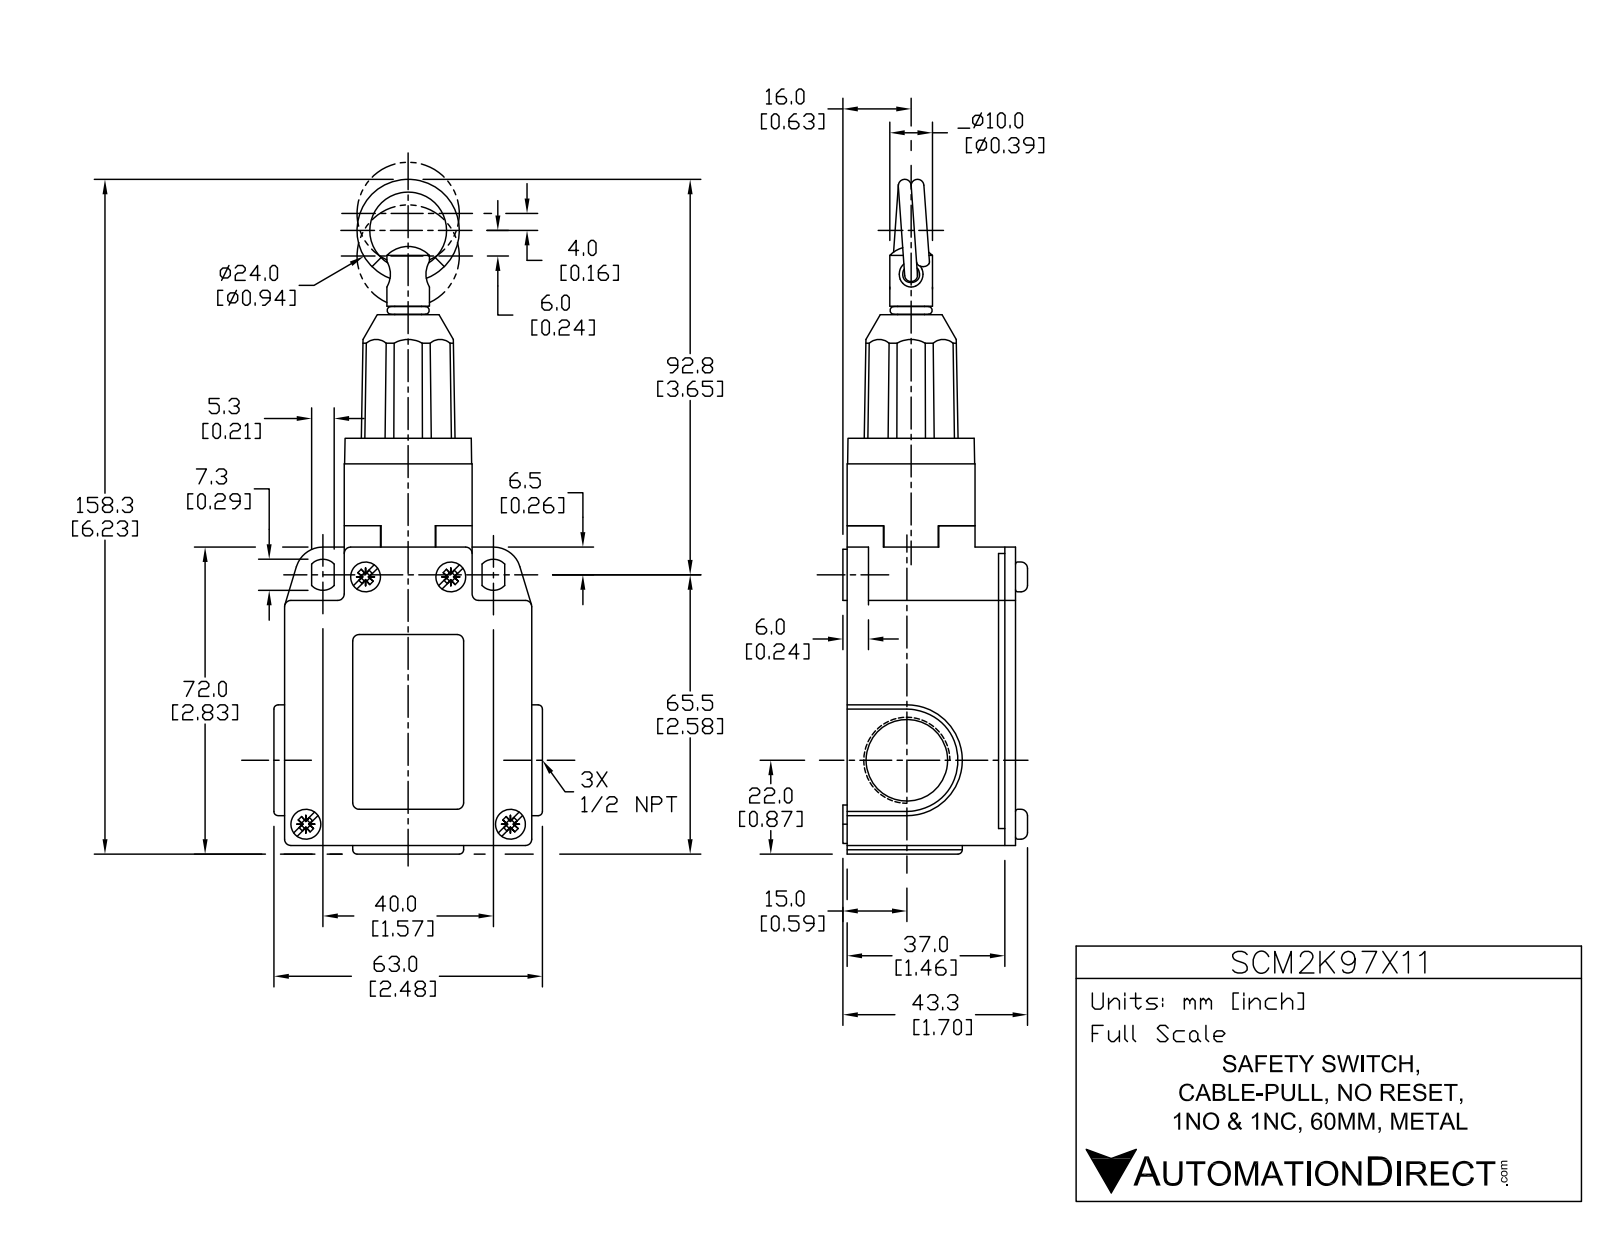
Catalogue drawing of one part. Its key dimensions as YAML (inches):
part_name: "SCM2K97X11"
step_written_by: "SolidWorks 2017 (AUTOMOTIVE_DESIGN)"
units: inches
bodies: {solids: 5, faces: 202, planar: 89, cylindrical: 88, other: 25}
overall_size: [6.28, 2.441, 1.705]
volume: 10.97
surface_area: 48.85
round_holes:
  - {diameter: 0.669, count: 2}
  - {diameter: 0.748, count: 2}
  - {diameter: 0.157, count: 1}
  - {diameter: 0.398, count: 1}
  - {diameter: 0.709, count: 1}
round_bosses_or_shafts:
  - {diameter: 0.276, count: 4}
  - {diameter: 0.472, count: 2}
  - {diameter: 0.354, count: 2}
  - {diameter: 0.701, count: 1}
  - {diameter: 0.394, count: 1}
  - {diameter: 0.248, count: 1}
partial_cylinders:
  - {radius: 0.059, count: 12}
  - {radius: 0.144, count: 2}
  - {radius: 0.256, count: 2}
  - {radius: 0.512, count: 2}
  - {radius: 0.453, count: 1}
  - {radius: 0.472, count: 1}
face_to_face_distances: [1.555, 0.551, 1.732, 1.181, 2.283, 0.079, 0.236, 0.157, 0.197, 2.756]
hole_center_spacings: [0.039, 4.528]
